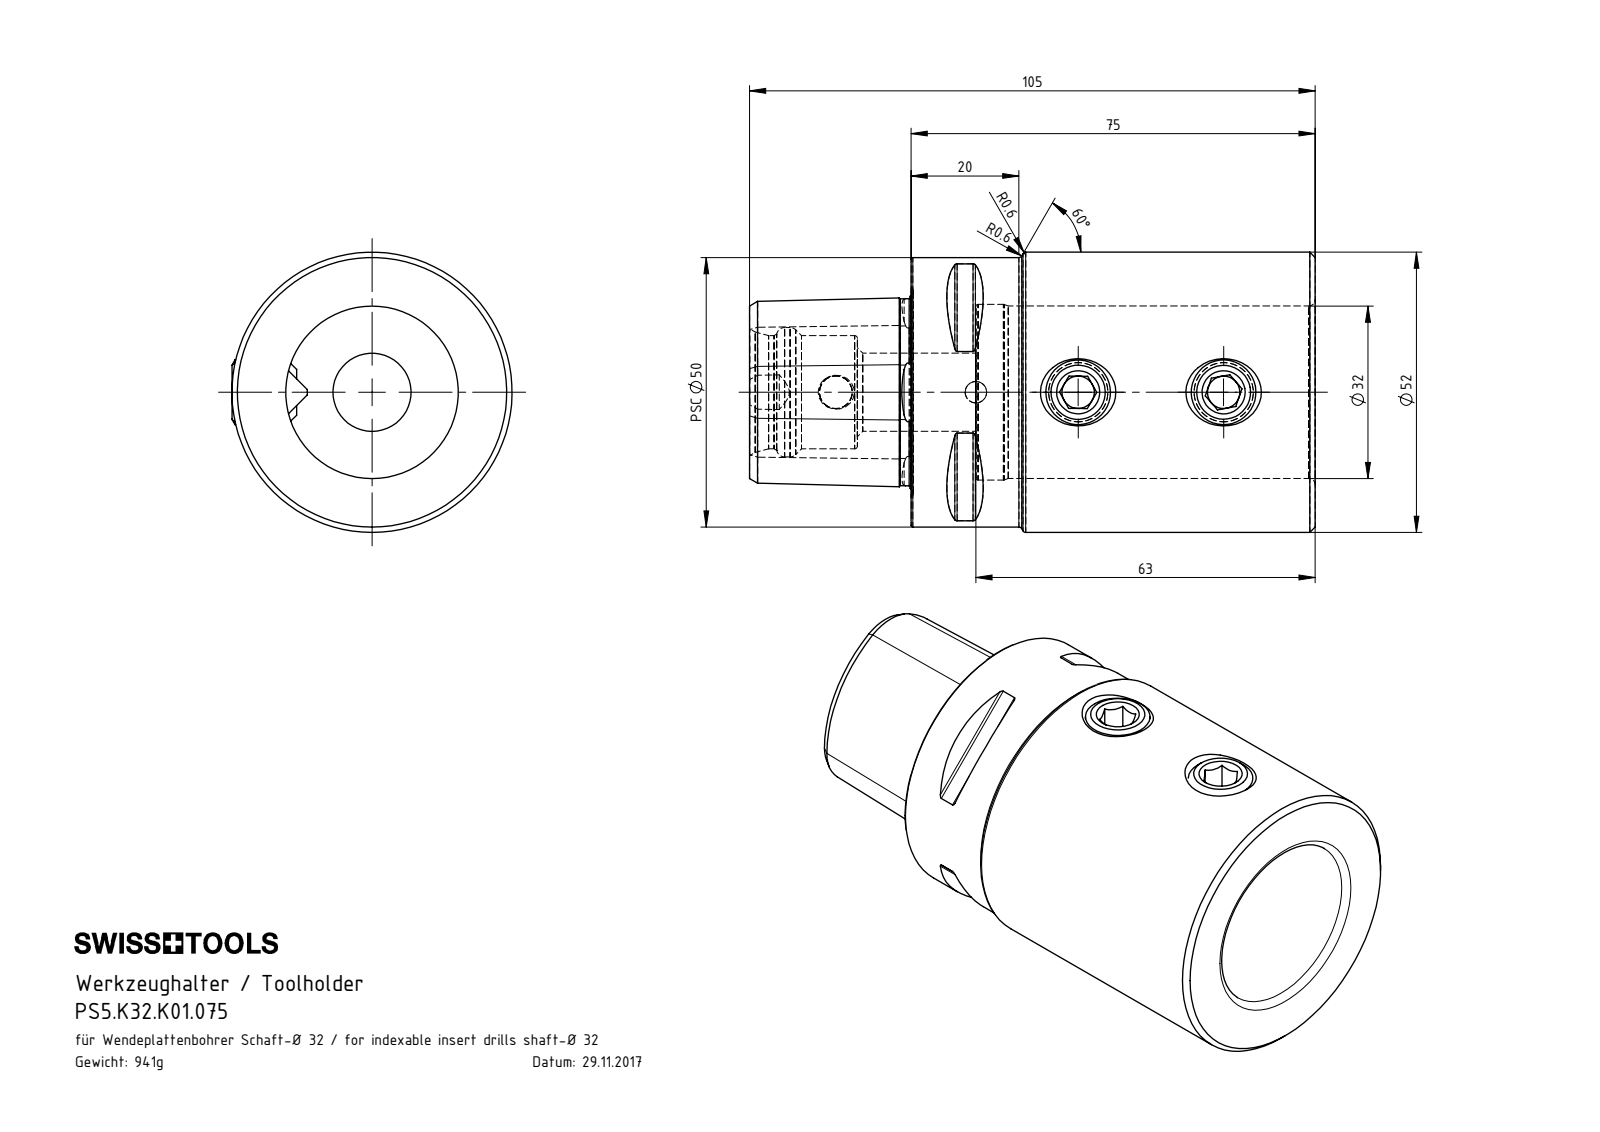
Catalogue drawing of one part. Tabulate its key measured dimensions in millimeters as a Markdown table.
| quantity | value |
| --- | --- |
| part name | K32-ER2.012.014; PS5-K32.K01.075_A; PS5.K32.K01.075; K32-ER1.012.012_M12x12 |
| STEP written by | SolidWorks 2017 (AUTOMOTIVE_DESIGN) |
| units | millimeters |
| bodies | 3 solids, 139 faces (48 planar, 26 cylindrical, 65 other) |
| overall size | 105 × 52 × 52 |
| volume | 119 884 mm³ |
| surface area | 29 768 mm² |
| round holes (diameter × count) | 6 × 2, 11 × 2, 4 × 1, 6.1 × 1, 14.5 × 1, 21 × 1, 24 × 1, 32 × 1, 32.6 × 1 |
| round bosses / shafts (diameter × count) | 12 × 2, 52 × 1, 50 × 1 |
| partial cylindrical surfaces (radius × count) | 0.5 × 8, 4 × 1 |
| main face-to-face distances | 75, 12, 63, 30, 42, 105, 19.18, 44.4, 6, 20 |
| hole center spacings | 19, 26, 27, 45, 46, 72 |
